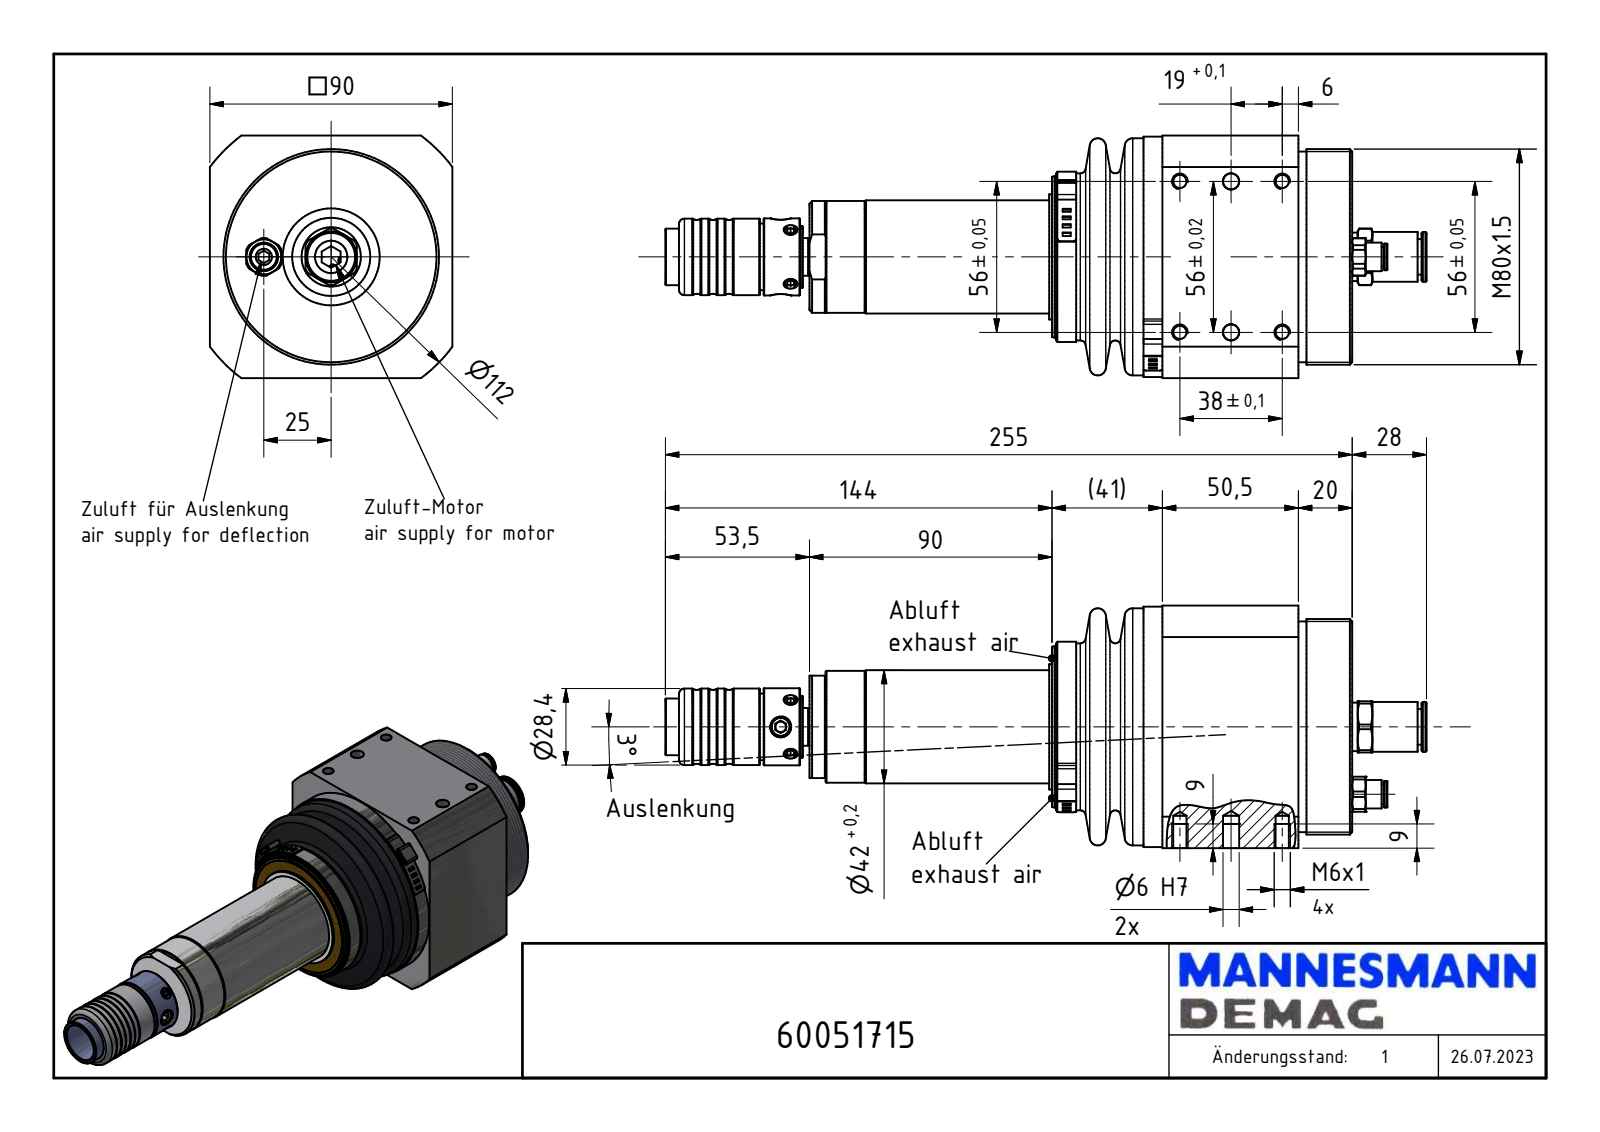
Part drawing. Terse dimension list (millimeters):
name: ESR 30 WS_60051715
written by: Autodesk Inventor 2014 (AUTOMOTIVE_DESIGN)
unit: mm
bodies: 24 solids, 914 faces (299 planar, 443 cylindrical, 172 other)
size: 282.55 × 90 × 90
volume: 1 027 000 mm³; area: 255 470 mm²
holes: 15× ⌀6, 4× ⌀4.92, 2× ⌀2.5, 2× ⌀3.5, 2× ⌀4, 2× ⌀4.13, 2× ⌀5, 1× ⌀5.6, 1× ⌀6.1, 1× ⌀6.19, 1× ⌀6.65, 1× ⌀8.05
bosses: 2× ⌀5, 1× ⌀89.2, 1× ⌀86, 1× ⌀85.5, 1× ⌀81.43, 1× ⌀78.16, 1× ⌀78, 1× ⌀73.28
rounds: 98× R4.65, 8× R0.5, 8× R1, 8× R1.1, 6× R10, 4× R1.4, 4× R2, 2× R2.5
face distances: 90, 54, 10, 3.5, 64.55, 70.5, 5.95, 16.5, 20, 4
hole spacings: 15, 7.76, 21.21, 25.98, 28.98, 30, 8.59, 13.05
